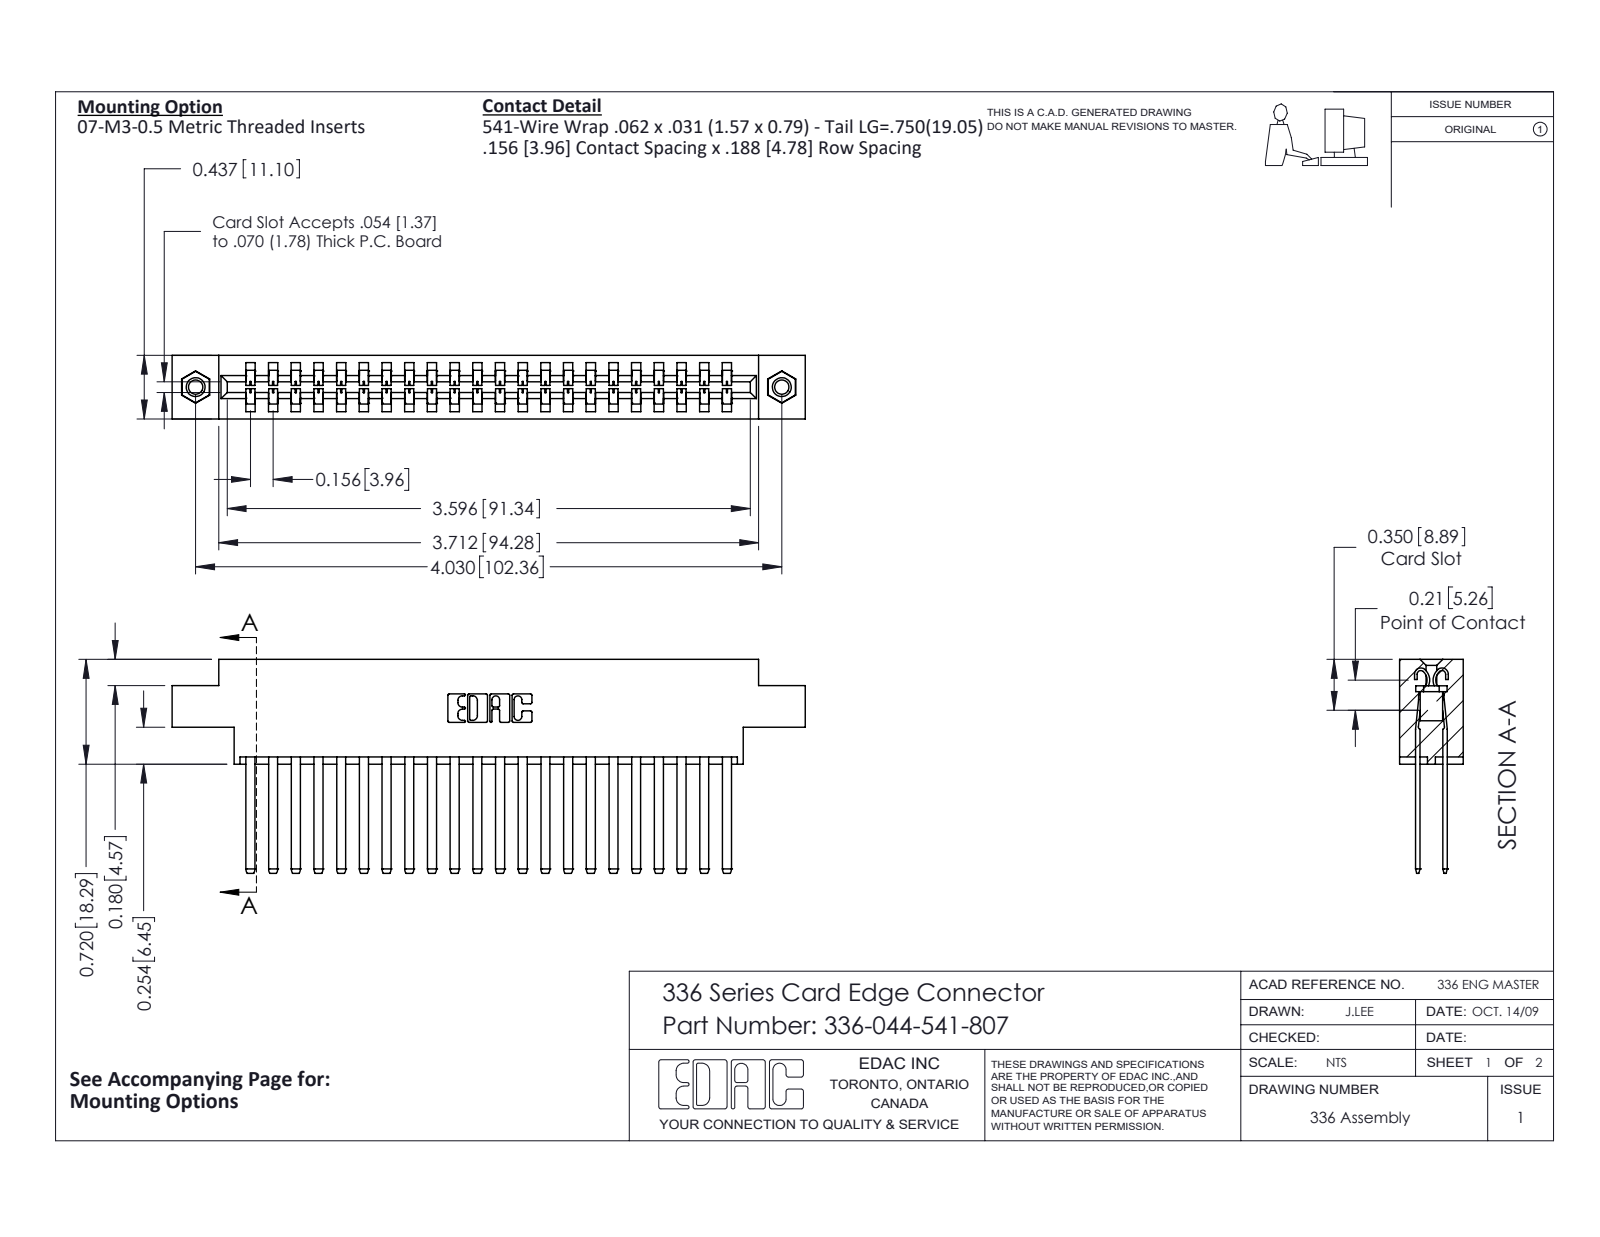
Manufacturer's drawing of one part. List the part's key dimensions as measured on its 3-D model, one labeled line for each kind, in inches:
Part name (STEP PRODUCT): 345-250-001_345-250-005-103; 336-290-001_336-290-541; 336 Part_Offset - .156 Dia - TI; 336-044-541-807
STEP written by: SolidWorks 2020 (CONFIG_CONTROL_DESIGN)
Units: inches
Bodies: 47 solids, 2026 faces (1250 planar, 760 cylindrical, 16 other)
Overall size (bounding box): 4.353 × 1.47 × 0.437
Volume: 1.001 in³ · Surface area: 32.08 in²
Round holes (diameter × count): ⌀0.098 ×2, ⌀0.125 ×2, ⌀0.156 ×2
Round bosses / shafts (diameter × count): ⌀0.155 ×2
Partial cylindrical surfaces — rounded edges, fillets, slot ends (radius × count): R0.004 ×88, R0.056 ×44, R0.01 ×22, R0.007 ×6, R0.031 ×6, R0.022 ×4, R0.04 ×4, R0.026 ×3
Main face-to-face distances: 0.188, 0.328, 0.14, 0.297, 0.109, 0.031, 0.437, 0.033, 0.156, 0.181
Hole centre spacings: 4.03
